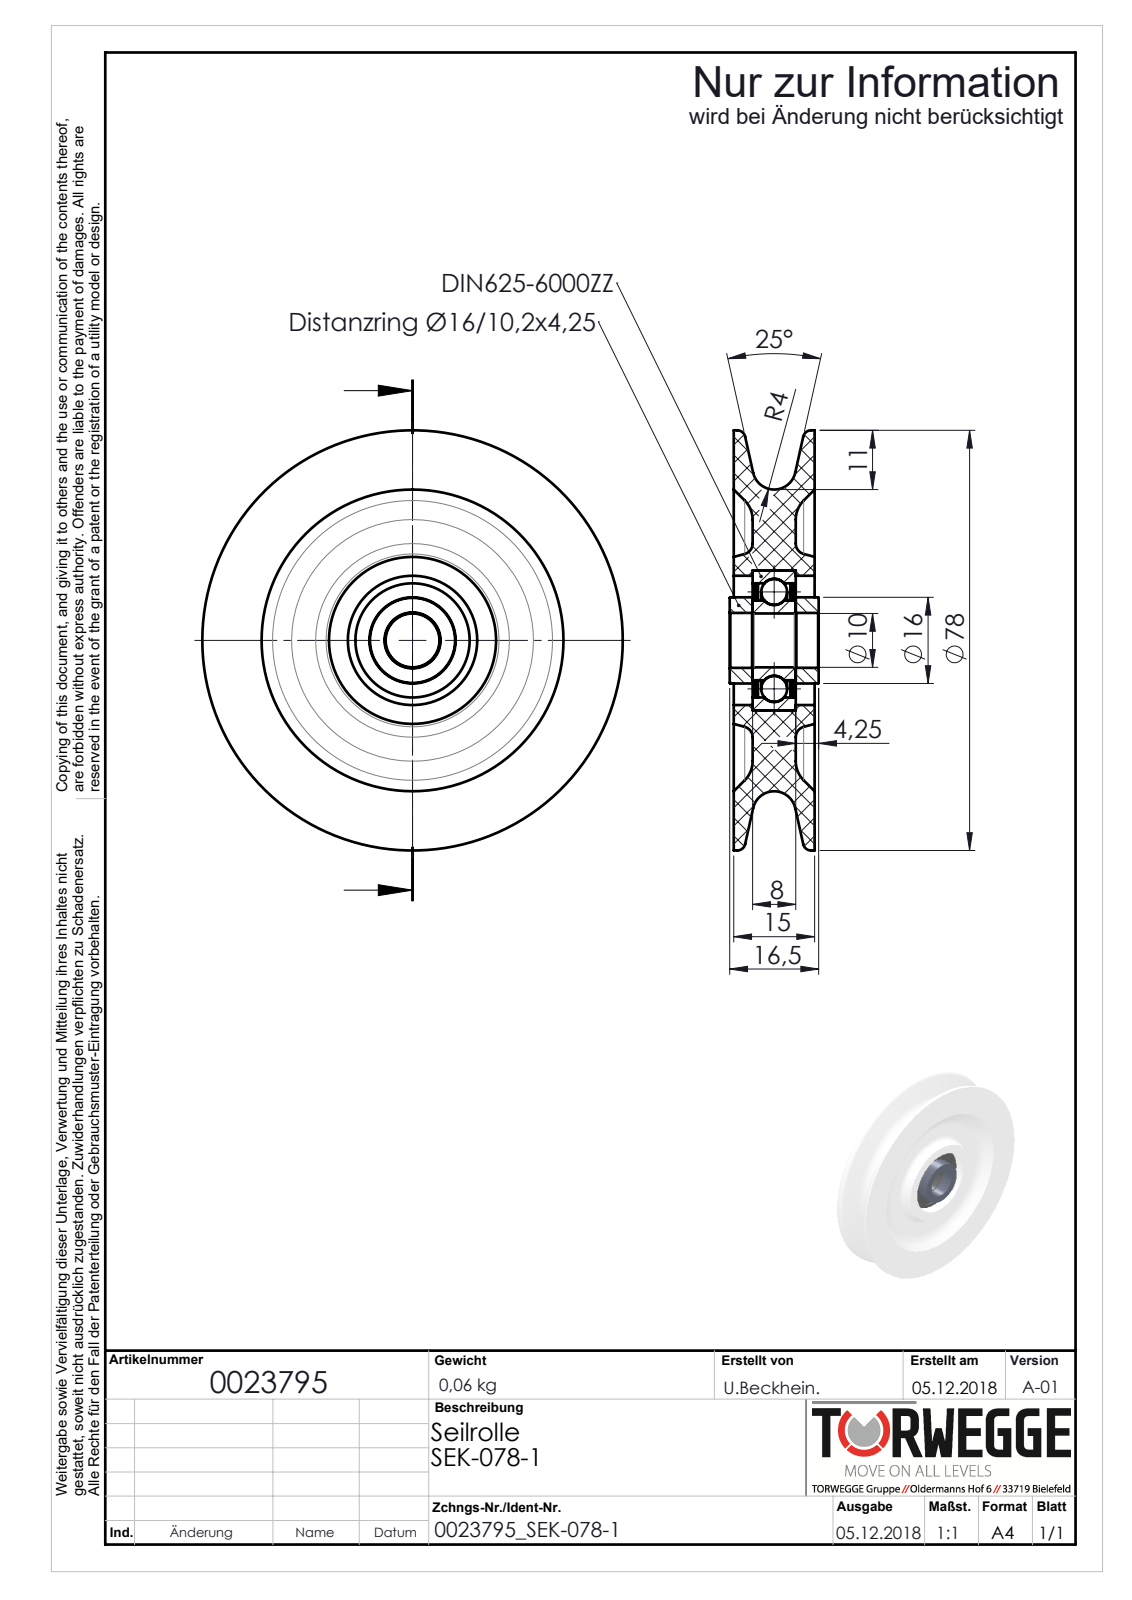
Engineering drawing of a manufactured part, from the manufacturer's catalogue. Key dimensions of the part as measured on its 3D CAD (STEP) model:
Part name (STEP PRODUCT): 0023795_SEK-078-1_(A-01)
STEP written by: SolidWorks 2018 (AUTOMOTIVE_DESIGN)
Units: millimetres
Bodies: 8 solids, 118 faces (20 planar, 38 cylindrical, 60 other)
Overall size (bounding box): 78 × 78 × 16.5
Volume: 38 859 mm³ · Surface area: 22 324 mm²
Round holes (diameter × count): ⌀10 ×1, ⌀10.2 ×1, ⌀14.8 ×1, ⌀21.2 ×1, ⌀24 ×1, ⌀26 ×1
Round bosses / shafts (diameter × count): ⌀78 ×1, ⌀16 ×1
Main face-to-face distances: 15, 3.5, 11.5, 8, 0.5, 7, 4, 4.5, 10.5, 11
